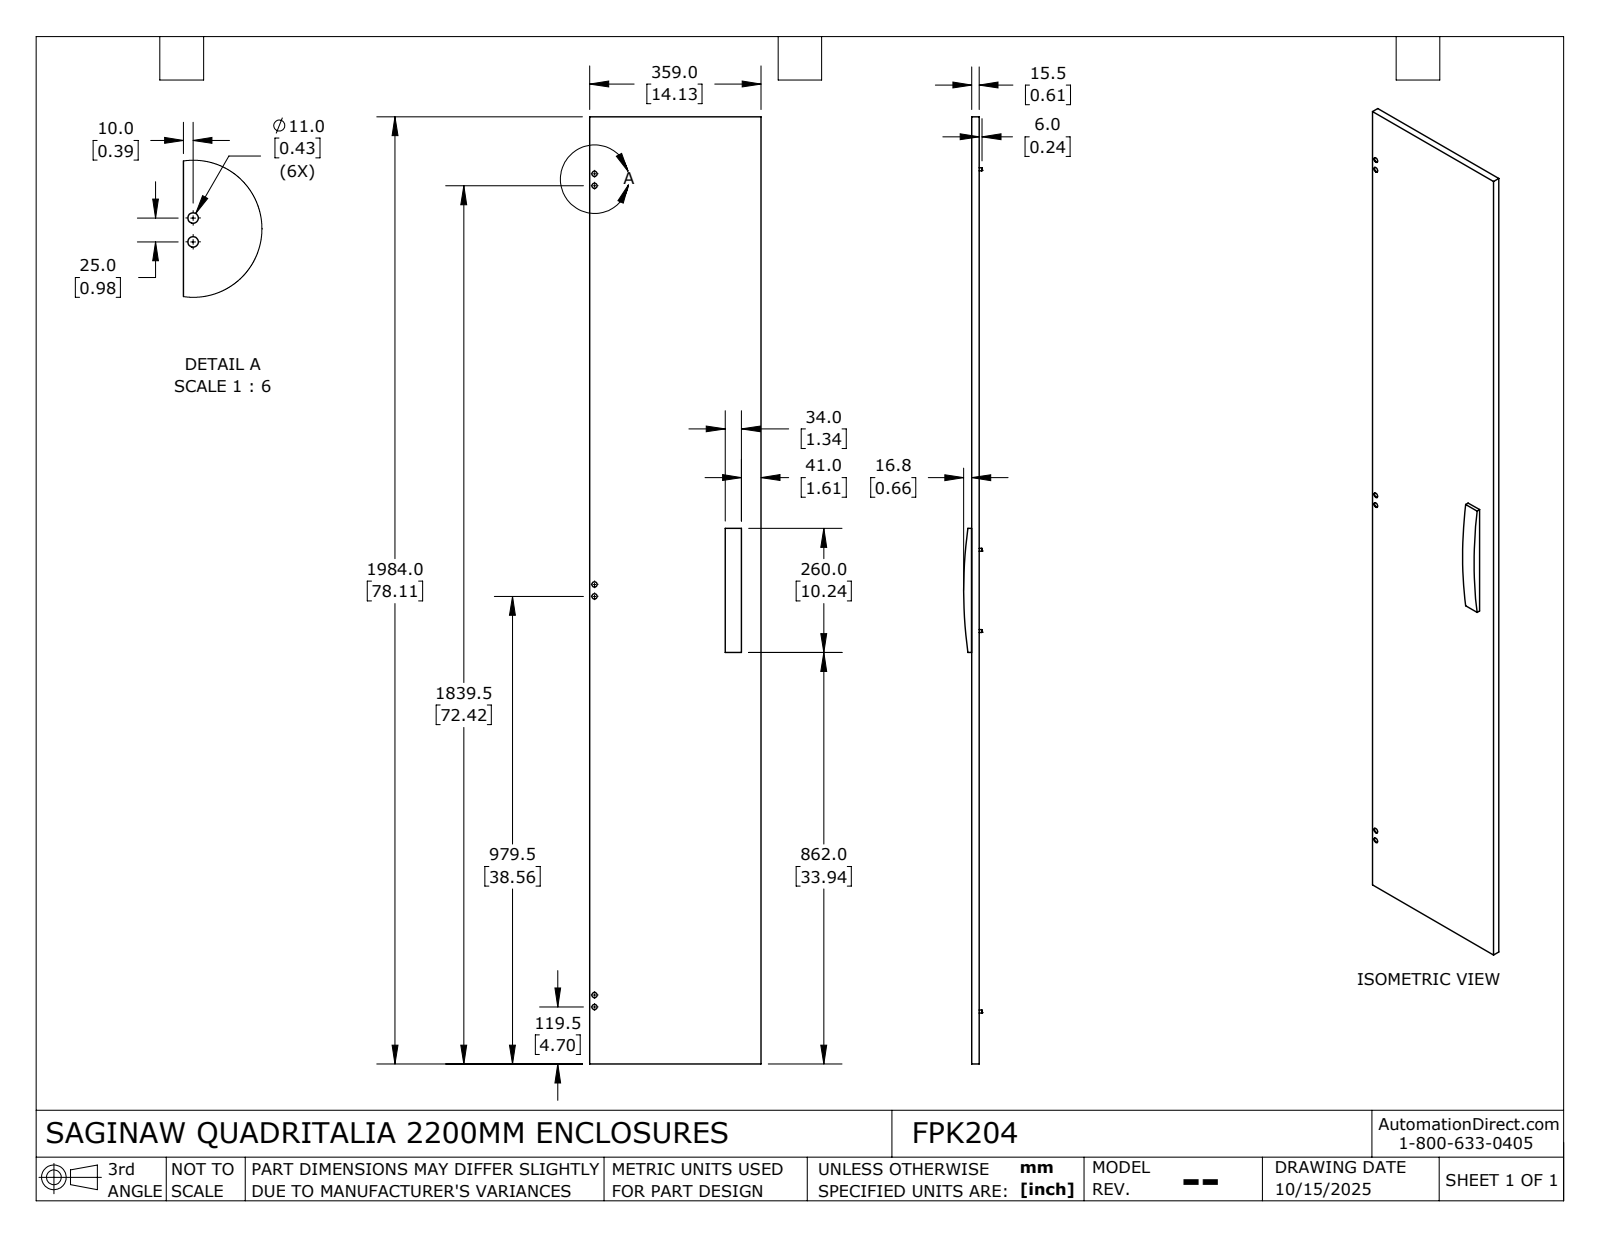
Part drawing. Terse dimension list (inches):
name: FPK204
written by: SolidWorks 2024 (AUTOMOTIVE_DESIGN)
unit: in
bodies: 2 solids, 48 faces (25 planar, 19 cylindrical, 4 other)
size: 78.11 × 14.134 × 1.509
volume: 100.4 in³; area: 2 514 in²
holes: 6× ⌀0.433
bosses: 4× ⌀0.276, 4× ⌀0.236
rounds: 4× R0.296, 1× R37.908
face distances: 0.059, 14.075, 14.134, 14.016, 78.051, 0.02, 0.079, 0.63, 0.61, 0.551
hole spacings: 33.858, 0.984, 32.874, 34.843, 67.717, 66.732, 68.701
